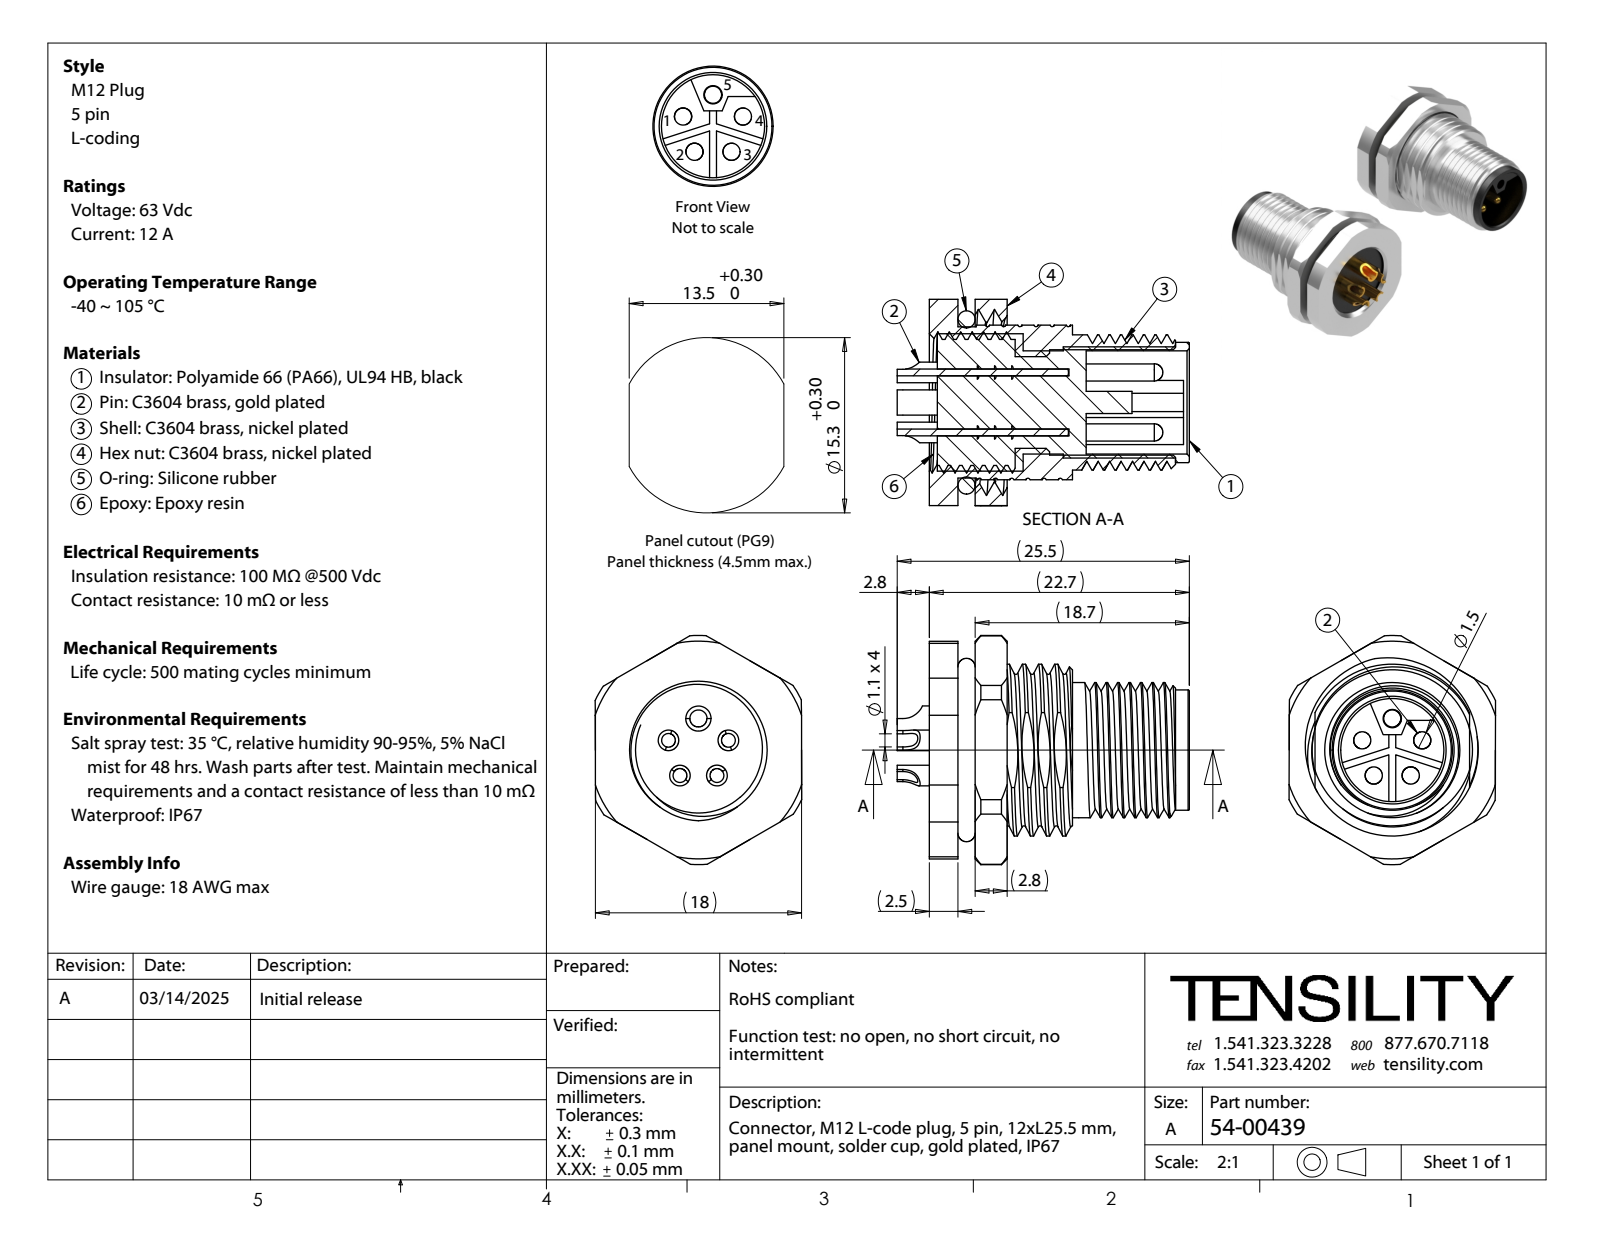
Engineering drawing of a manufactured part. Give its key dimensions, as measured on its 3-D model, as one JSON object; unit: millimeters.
{"part_name": "54-00439-05; 54-00439-01; 54-00439-06; 54-00439-02 (+3 more)", "step_written_by": "SolidWorks 2021 (CONFIG_CONTROL_DESIGN)", "units": "millimeters", "bodies": {"solids": 9, "faces": 370, "planar": 107, "cylindrical": 157, "other": 106}, "overall_size": [25.5, 20, 18.03], "volume_mm3": 3270, "surface_area_mm2": 6018, "round_holes": [[1.5, 5], [1.2, 4], [1.6, 1], [8, 1], [9, 1], [9.2, 1], [11, 1], [14, 1]], "round_bosses_or_shafts": [[1.8, 4], [13.2, 1], [12, 1], [11.8, 1], [10.5, 1], [9.7, 1], [2.2, 1]], "partial_cylinders_radius": [[1.7, 4], [1.86, 1], [7.5, 1], [9.5, 1], [10, 1]], "face_to_face_distances": [0.7, 6.8, 2.5, 4.3, 18, 4, 7.5, 1.8, 5, 1.5], "hole_center_spacings": [2.75, 5.23, 3.24, 3.23, 5.24]}
